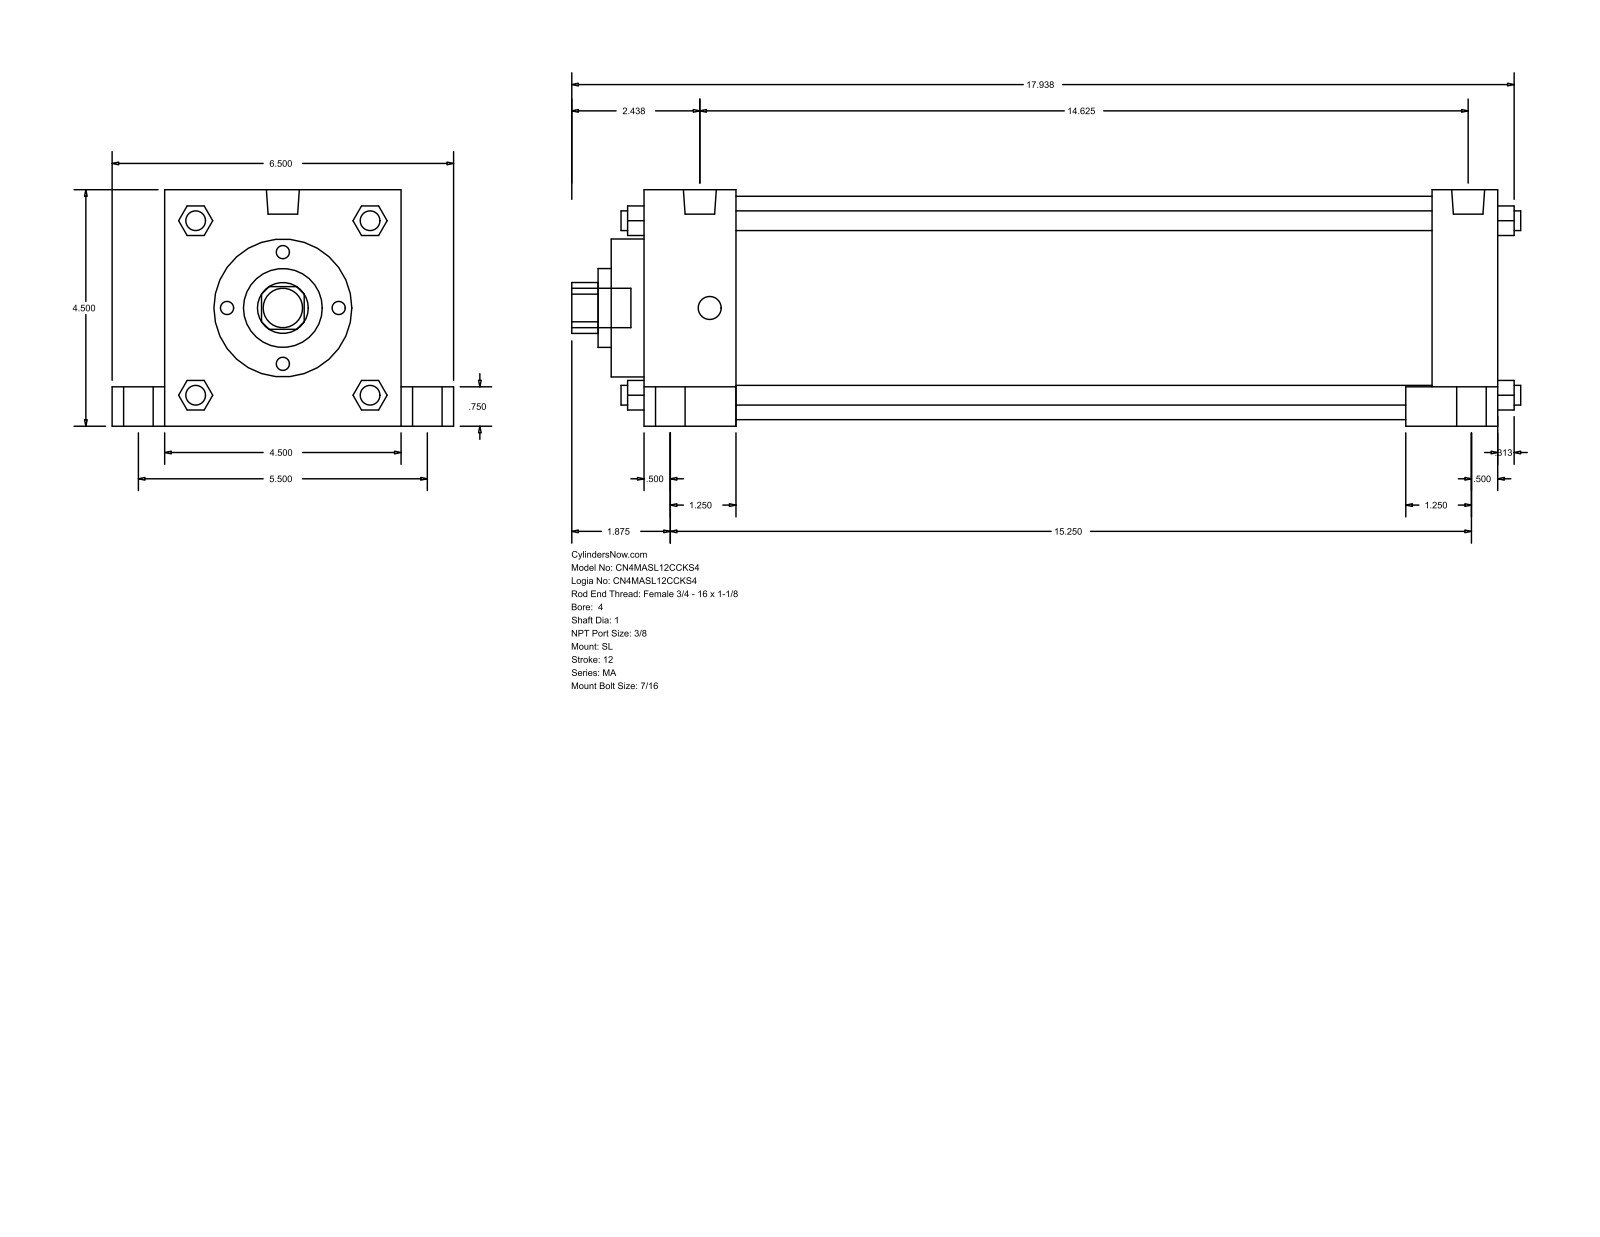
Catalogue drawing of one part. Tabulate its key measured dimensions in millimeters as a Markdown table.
| quantity | value |
| --- | --- |
| part name | MA_SL__0400_1 |
| STEP written by | GSSL Pune (CONFIG_CONTROL_DESIGN) |
| units | millimeters |
| bodies | 0 solids, 150 faces (113 planar, 37 cylindrical, 0 other) |
| overall size | 458.79 × 165.1 × 114.3 |
| round holes (diameter × count) | 25.4 × 1, 38.1 × 1, 66.67 × 1, 107.95 × 1 |
| round bosses / shafts (diameter × count) | 20.64 × 4, 14.29 × 4, 11.11 × 4, 9.53 × 4, 15.93 × 2, 19.05 × 1 |
| partial cylindrical surfaces (radius × count) | 12.29 × 1 |
| main face-to-face distances | 114.3, 412.76, 336.55, 44.46, 368.3, 381.01, 31.75, 25.4, 139.7, 19.05 |
